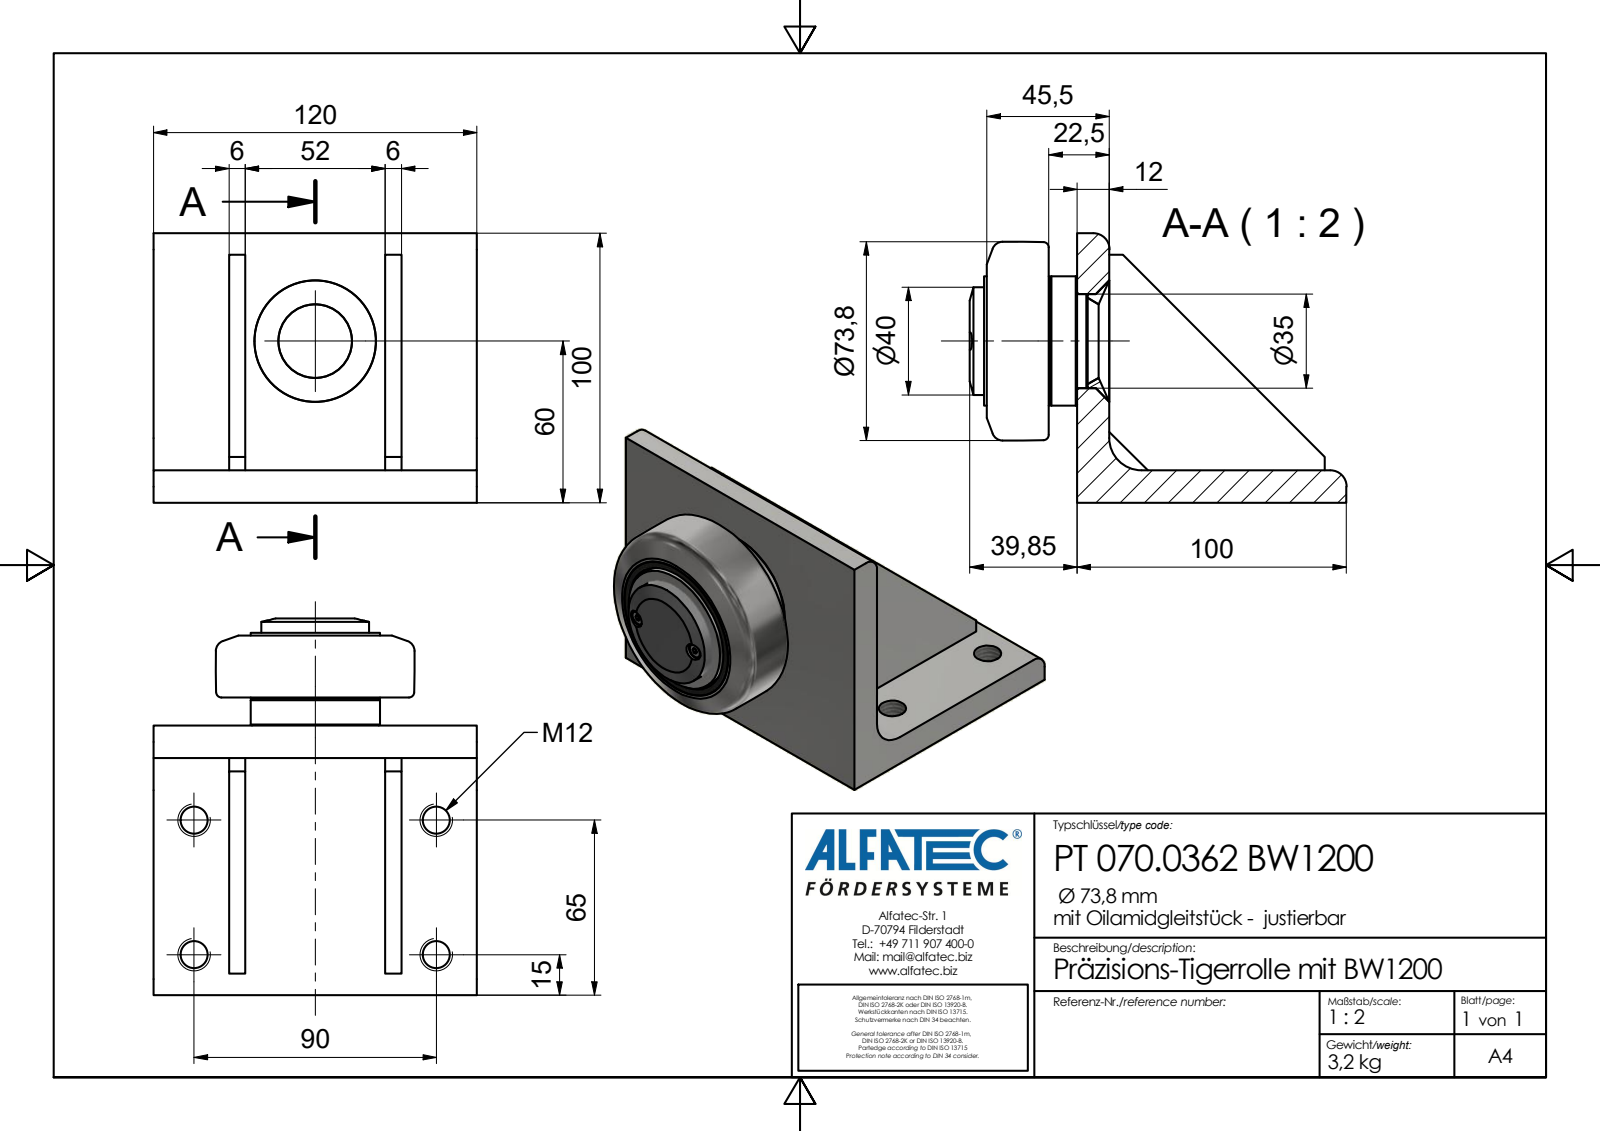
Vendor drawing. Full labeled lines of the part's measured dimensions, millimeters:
Part name (STEP PRODUCT): PT 070.0362 BW1200_Kontur
STEP written by: Autodesk Inventor 2020 (AP242_MANAGED_MODEL_BASED_3D_ENGINEERING_MIM_LF)
Units: millimetres
Bodies: 1 solid, 67 faces (42 planar, 15 cylindrical, 10 other)
Overall size (bounding box): 139.85 × 120 × 100
Volume: 428 362 mm³ · Surface area: 78 107 mm²
Round holes (diameter × count): ⌀10.11 ×4, ⌀6.5 ×2
Round bosses / shafts (diameter × count): ⌀5.35 ×2, ⌀48 ×1, ⌀40 ×1
Partial cylindrical surfaces — rounded edges, fillets, slot ends (radius × count): R6 ×2, R12 ×1
Main face-to-face distances: 12, 6, 58, 92, 28, 34, 86, 64, 52, 120
Hole centre spacings: 50, 90, 102.96, 30
